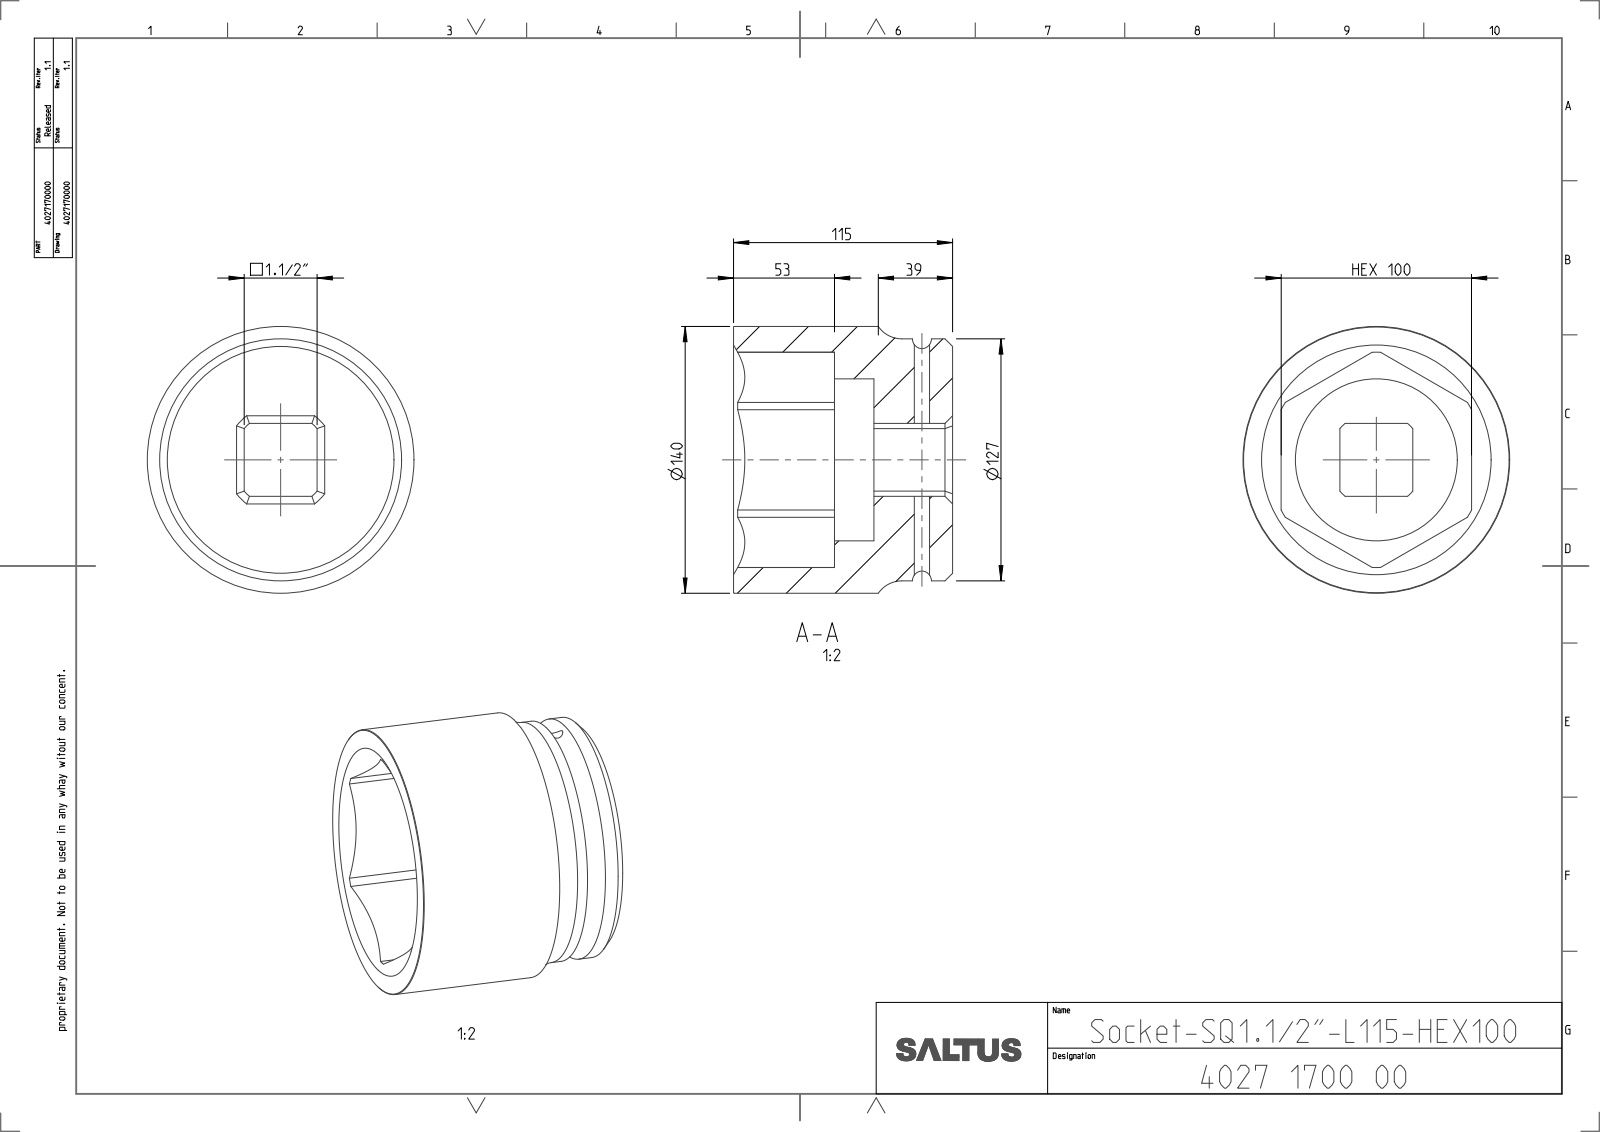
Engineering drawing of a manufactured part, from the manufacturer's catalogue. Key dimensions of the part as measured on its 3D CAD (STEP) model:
Part name (STEP PRODUCT): 4027170000
STEP written by: CREO PARAMETRIC BY PTC INC, 2022414 (CONFIG_CONTROL_DESIGN)
Units: millimetres
Bodies: 1 solid, 54 faces (18 planar, 22 cylindrical, 14 other)
Overall size (bounding box): 140 × 140 × 115
Volume: 1 008 000 mm³ · Surface area: 106 268 mm²
Round holes (diameter × count): ⌀8 ×1, ⌀85 ×1
Round bosses / shafts (diameter × count): ⌀140 ×1, ⌀127 ×1
Partial cylindrical surfaces — rounded edges, fillets, slot ends (radius × count): R25.2 ×1, R56.5 ×1
Main face-to-face distances: 100, 41.3, 115, 73.7, 62, 20.7, 53, 30.86, 69.14, 38.28
